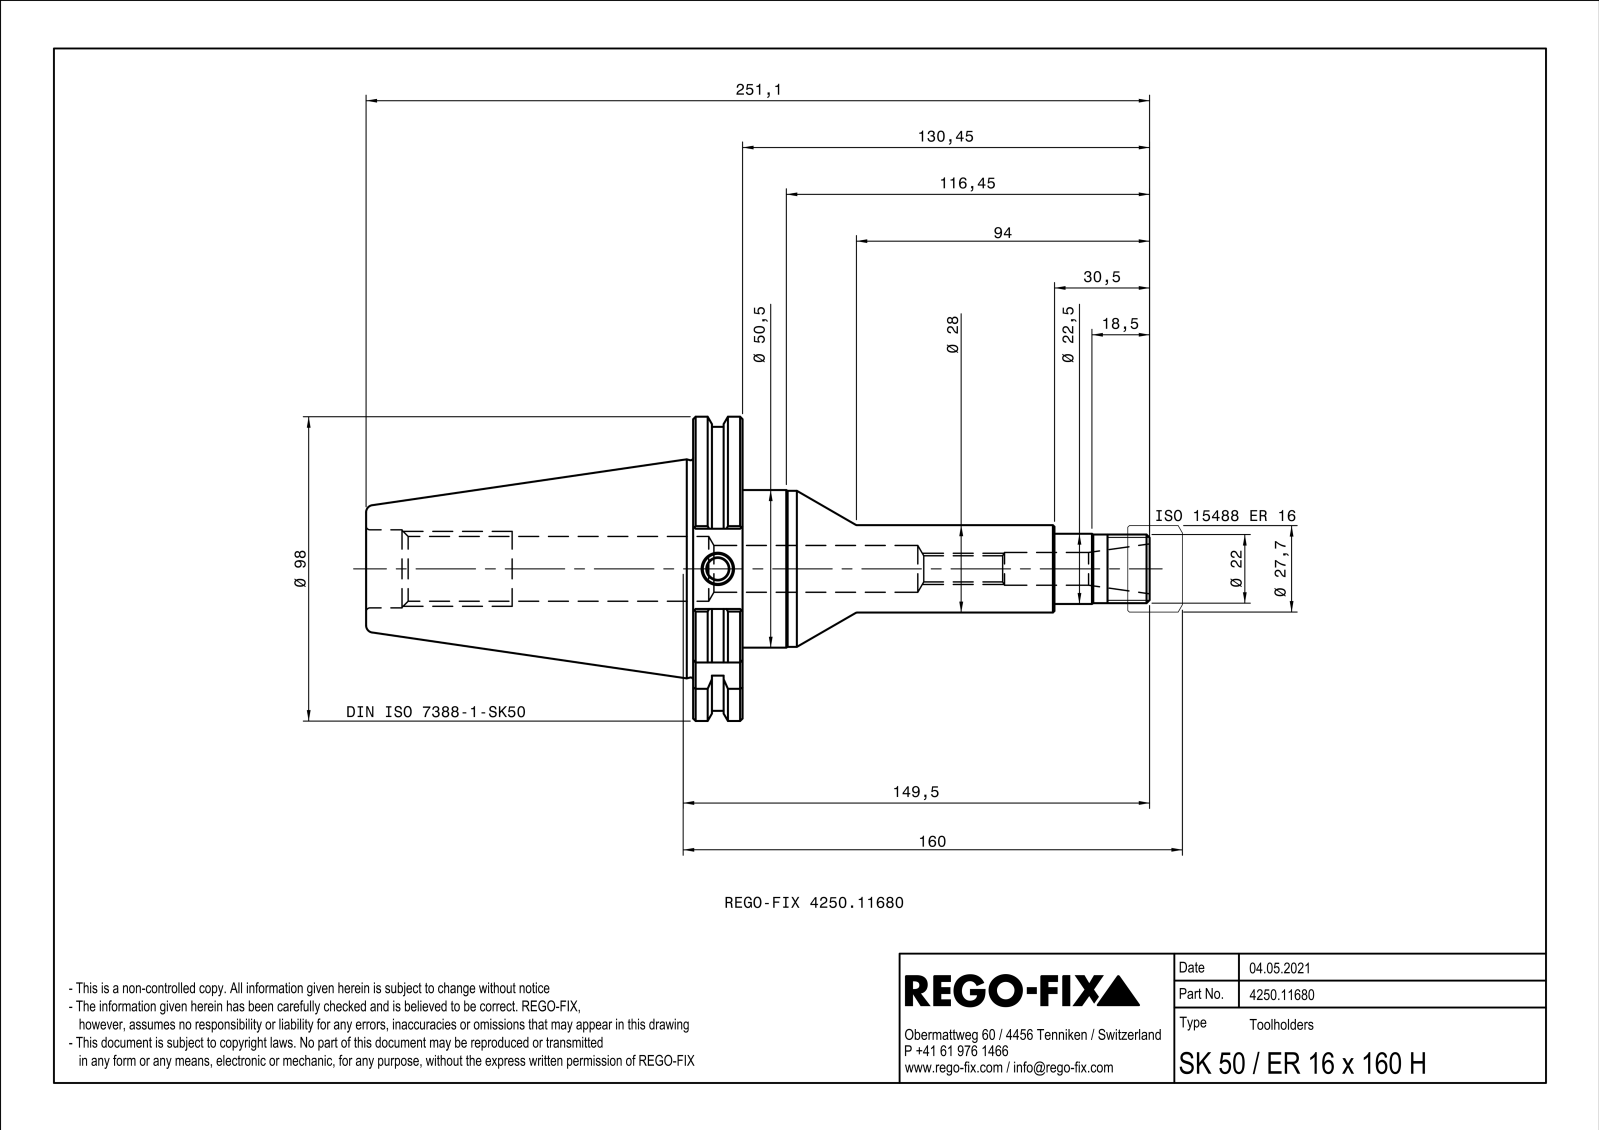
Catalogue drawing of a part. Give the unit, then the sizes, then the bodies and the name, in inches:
Units: inches
Overall size (bounding box): 9.886 × 3.839 × 3.684
Round holes (diameter × count): ⌀0.138 ×5, ⌀0.276 ×1, ⌀0.33 ×1, ⌀0.394 ×1, ⌀0.413 ×1, ⌀0.591 ×1, ⌀0.817 ×1, ⌀0.984 ×1
Round bosses / shafts (diameter × count): ⌀1.988 ×1, ⌀1.969 ×1, ⌀1.102 ×1, ⌀0.886 ×1, ⌀0.866 ×1
Partial cylindrical surfaces — rounded edges, fillets, slot ends (radius × count): R0.02 ×5, R1.791 ×1, R1.919 ×1
Main face-to-face distances: 0.624, 4.75, 4.126, 2.866, 1.012, 0.239, 0.385, 4.511, 0.387, 0.148
Volume: 25.25 in³ · Surface area: 93.84 in²
Bodies: 1 solid, 147 faces (42 planar, 42 cylindrical, 63 other)
Part name (STEP PRODUCT): NOCUT
STEP written by: SIEMENS PLM Software Solid Edge ST10 (AUTOMOTIVE_DESIGN)
